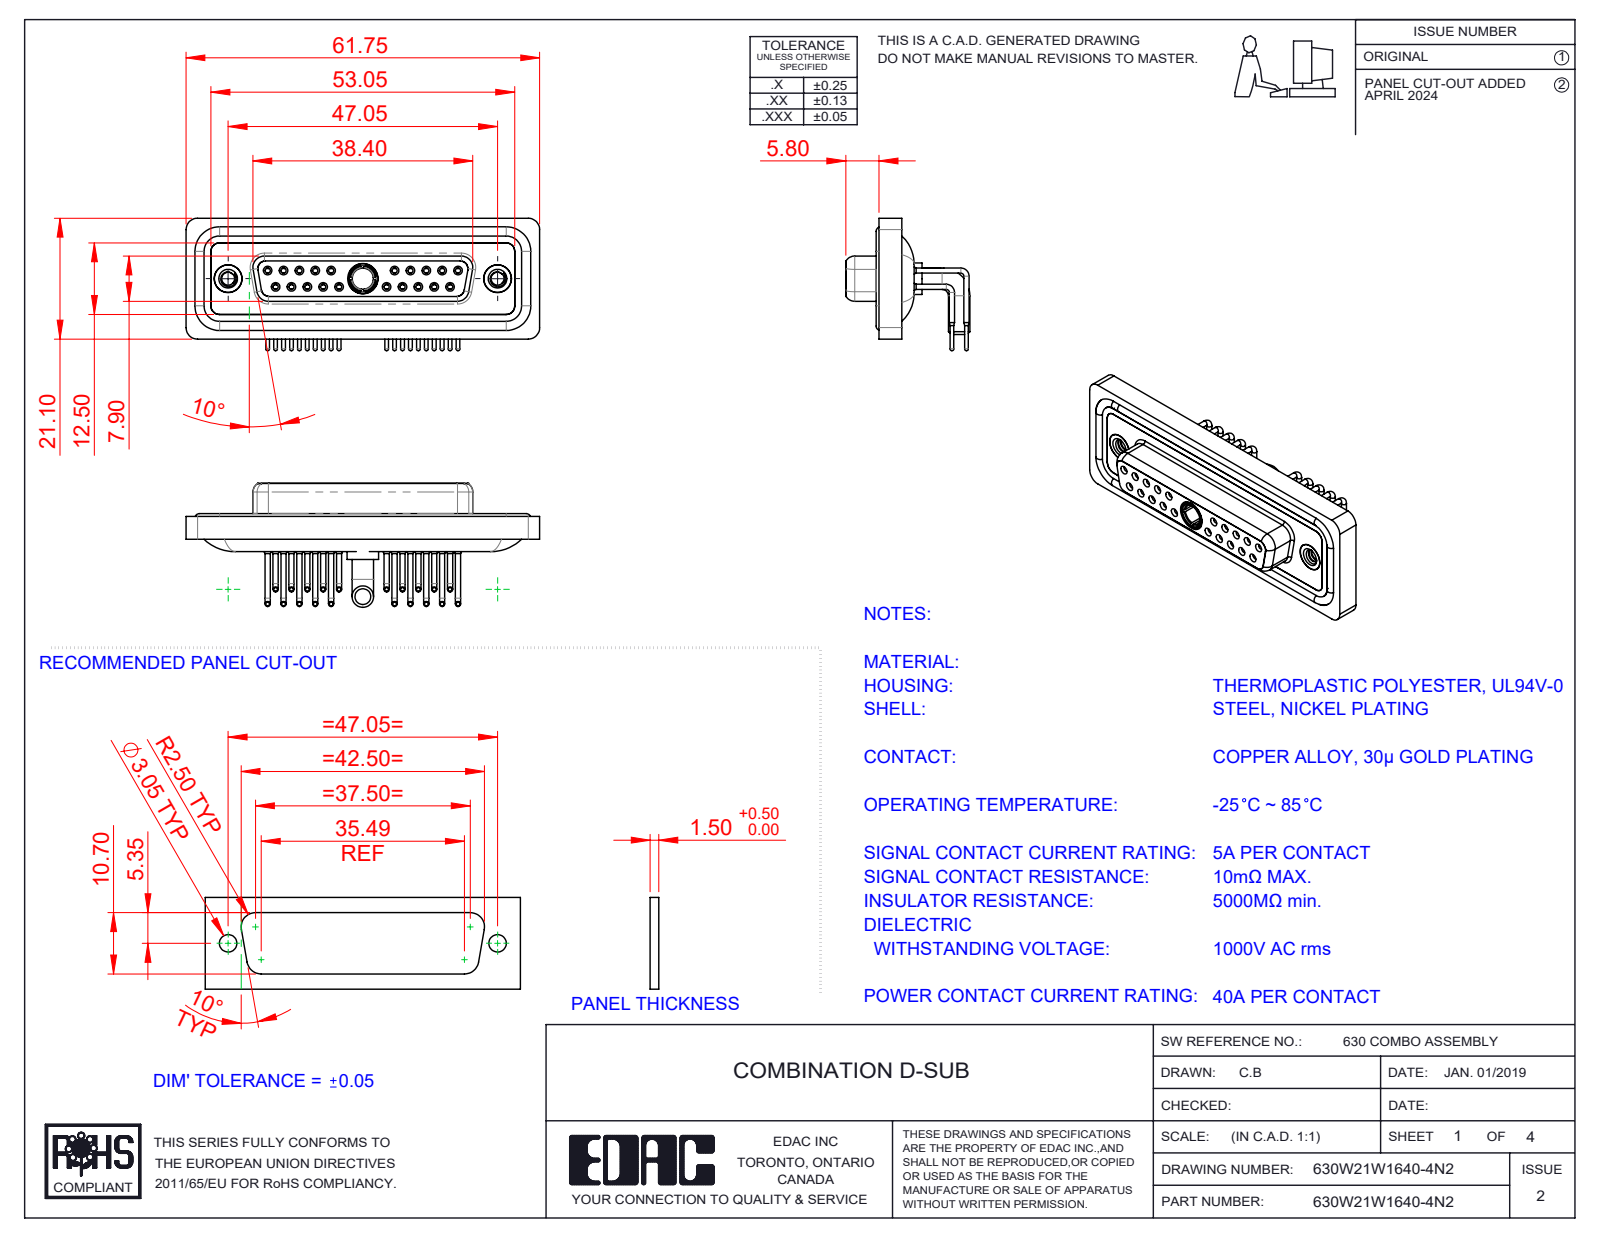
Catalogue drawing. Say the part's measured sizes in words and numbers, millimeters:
The part is named "630Combo Housing_21W1; 630Combo Waterproof Housing_25 Contacts; 630Combo Shell Rear_25 Contacts; 630Combo Shell Front_25 Contacts (+5 more)". Its 3-D file was written by "SolidWorks 2023 (CONFIG_CONTROL_DESIGN)". It is 29 solids with 1524 faces: 434 planar, 673 cylindrical and 417 other. Overall it measures 61.75 by 23.12 by 21.68 millimeters. Its volume is 8 578 cubic millimeters and its surface area 14 823 square millimeters. Round holes: 20 of diameter 0.9, 20 of diameter 1.1, 20 of diameter 1.5, 20 of diameter 2, 10 of diameter 1.6, 10 of diameter 1.7, 3 of diameter 4.85, 2 of diameter 2.26, 2 of diameter 4, 2 of diameter 4.05, 2 of diameter 5, 1 of diameter 3.7. Round bosses or shafts: 20 of diameter 0.9, 20 of diameter 0.65, 14 of diameter 1.6, 2 of diameter 4.95, 2 of diameter 4.8, 2 of diameter 3.75, 1 of diameter 5.5, 1 of diameter 5.2. Partial cylindrical surfaces (rounded edges, fillets, slot ends): 18 of radius 1.5, 18 of radius 2, 8 of radius 1.35, 8 of radius 1.6, 4 of radius 0.25, 4 of radius 0.5, 4 of radius 0.6, 4 of radius 0.65. The main face-to-face distances are 0.4, 1.8, 4.1, 1.6, 1.1, 2.5, 3.1, 1.5, 9.8, 0.45. The hole center spacings are 3.16, 2.77, 5.54, 8.31, 5.04, 19.39, 20.97, 22.16.
